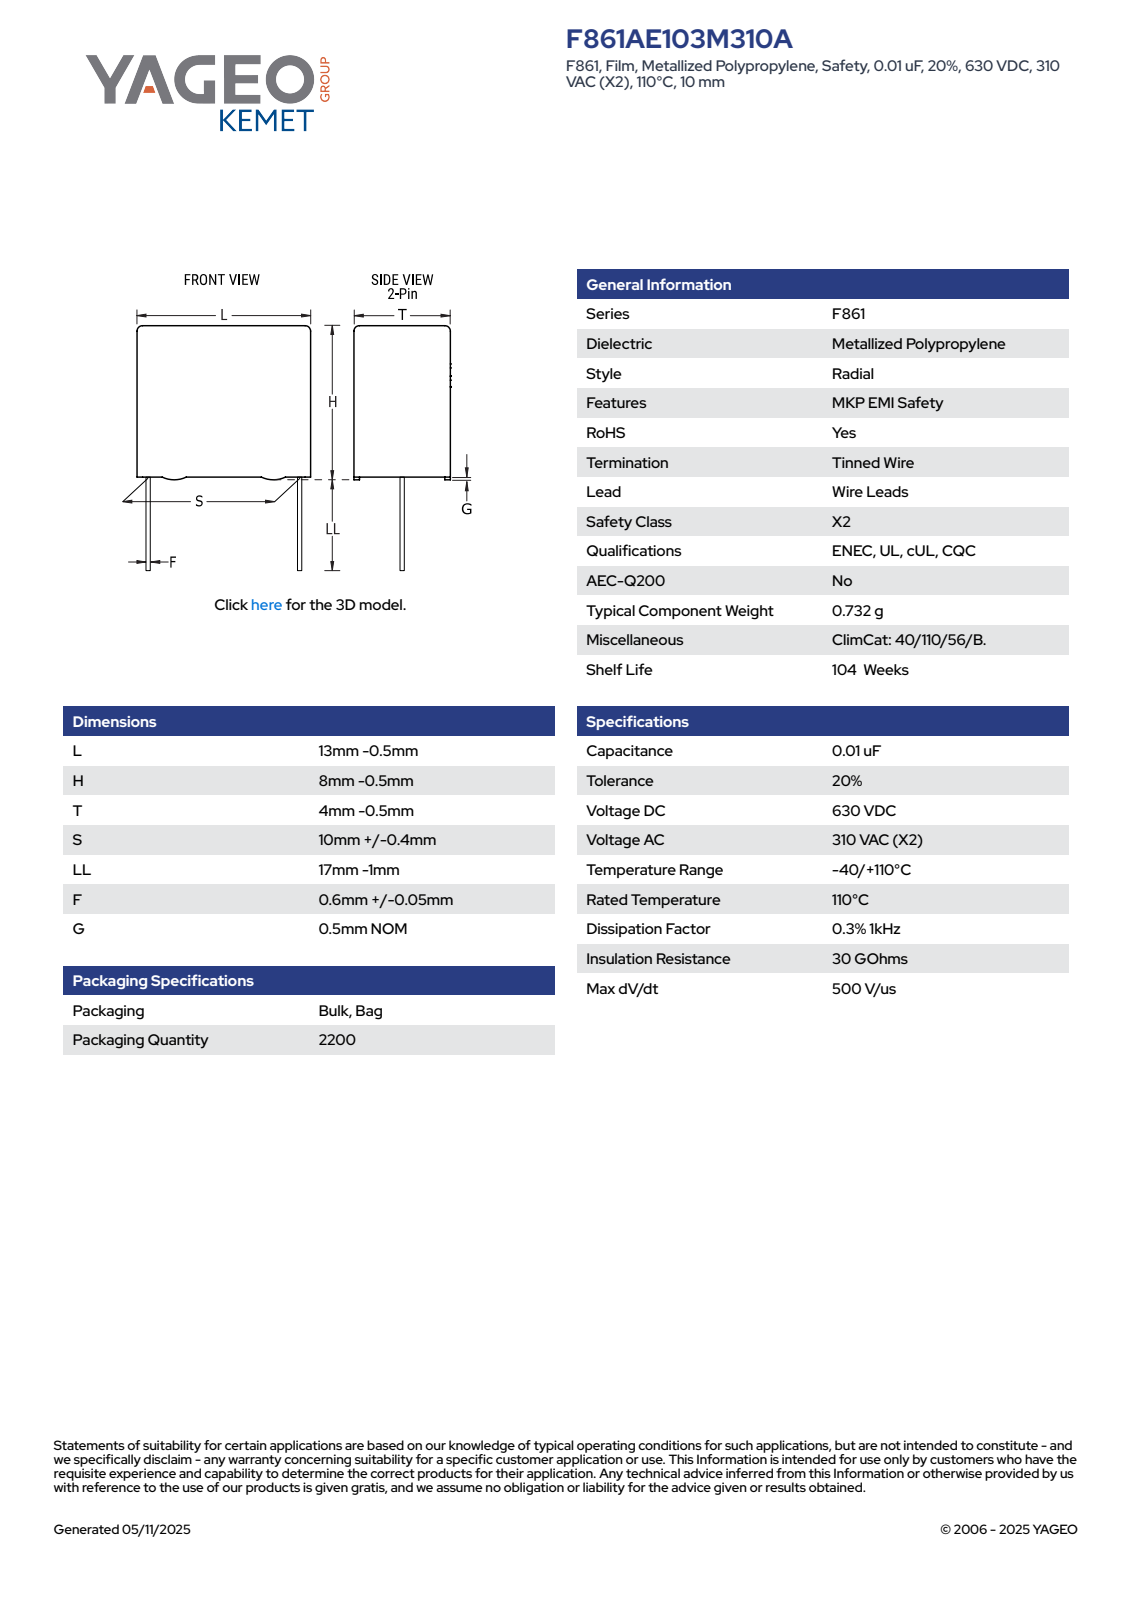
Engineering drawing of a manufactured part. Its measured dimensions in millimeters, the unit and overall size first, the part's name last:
Units: millimetres
Overall size (bounding box): 23.5 × 12.5 × 3.5
Round bosses / shafts (diameter × count): ⌀0.65 ×2
Partial cylindrical surfaces — rounded edges, fillets, slot ends (radius × count): R0.5 ×4
Main face-to-face distances: 3.5, 7, 12.5, 3.3, 3.1, 0.5, 7.5, 16, 16.5, 23.5
Volume: 316 mm³ · Surface area: 398 mm²
Bodies: 4 solids, 89 faces (81 planar, 8 cylindrical, 0 other)
Part name (STEP PRODUCT): CFR_RBG_13X8X4_L12.5H7.5T3.5S10LL16F0.65G0.5
STEP written by: SolidWorks 2014 (AUTOMOTIVE_DESIGN)
